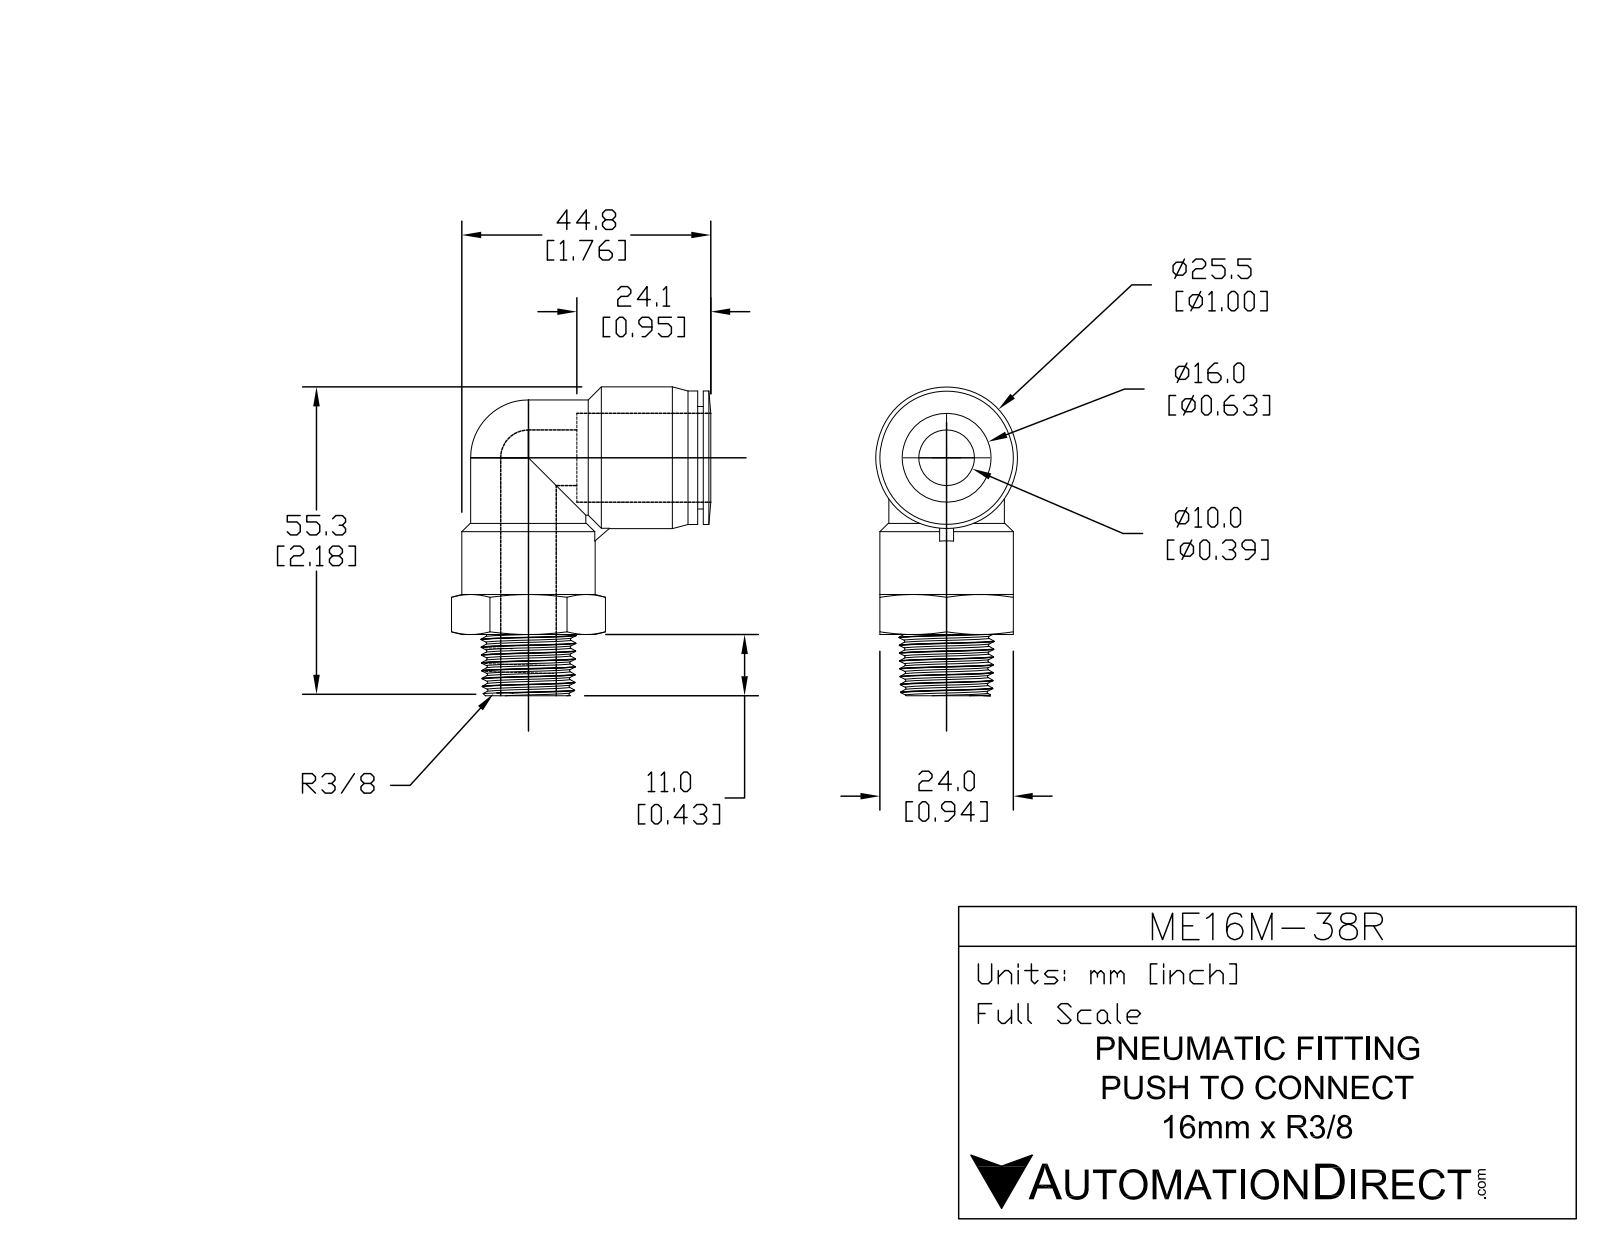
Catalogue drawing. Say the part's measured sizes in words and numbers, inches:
The part is named "ME16M-38R". Its 3-D file was written by "SolidWorks 2015 (AUTOMOTIVE_DESIGN)". It is 1 solid with 72 faces: 14 planar, 22 cylindrical and 36 other. Overall it measures 2.187 by 1.837 by 1.004 inches. Its volume is 1.223 cubic inches and its surface area 14.44 square inches. Round holes: 2 of diameter 0.394, 1 of diameter 0.642. Round bosses or shafts: 2 of diameter 0.803, 1 of diameter 1.004, 1 of diameter 0.992, 1 of diameter 0.984, 1 of diameter 0.945, 1 of diameter 0.709. The main face-to-face distances are 0.945, 0.839, 0.776, 0.063, 0.433, 0.423, 0.522, 0.098.
